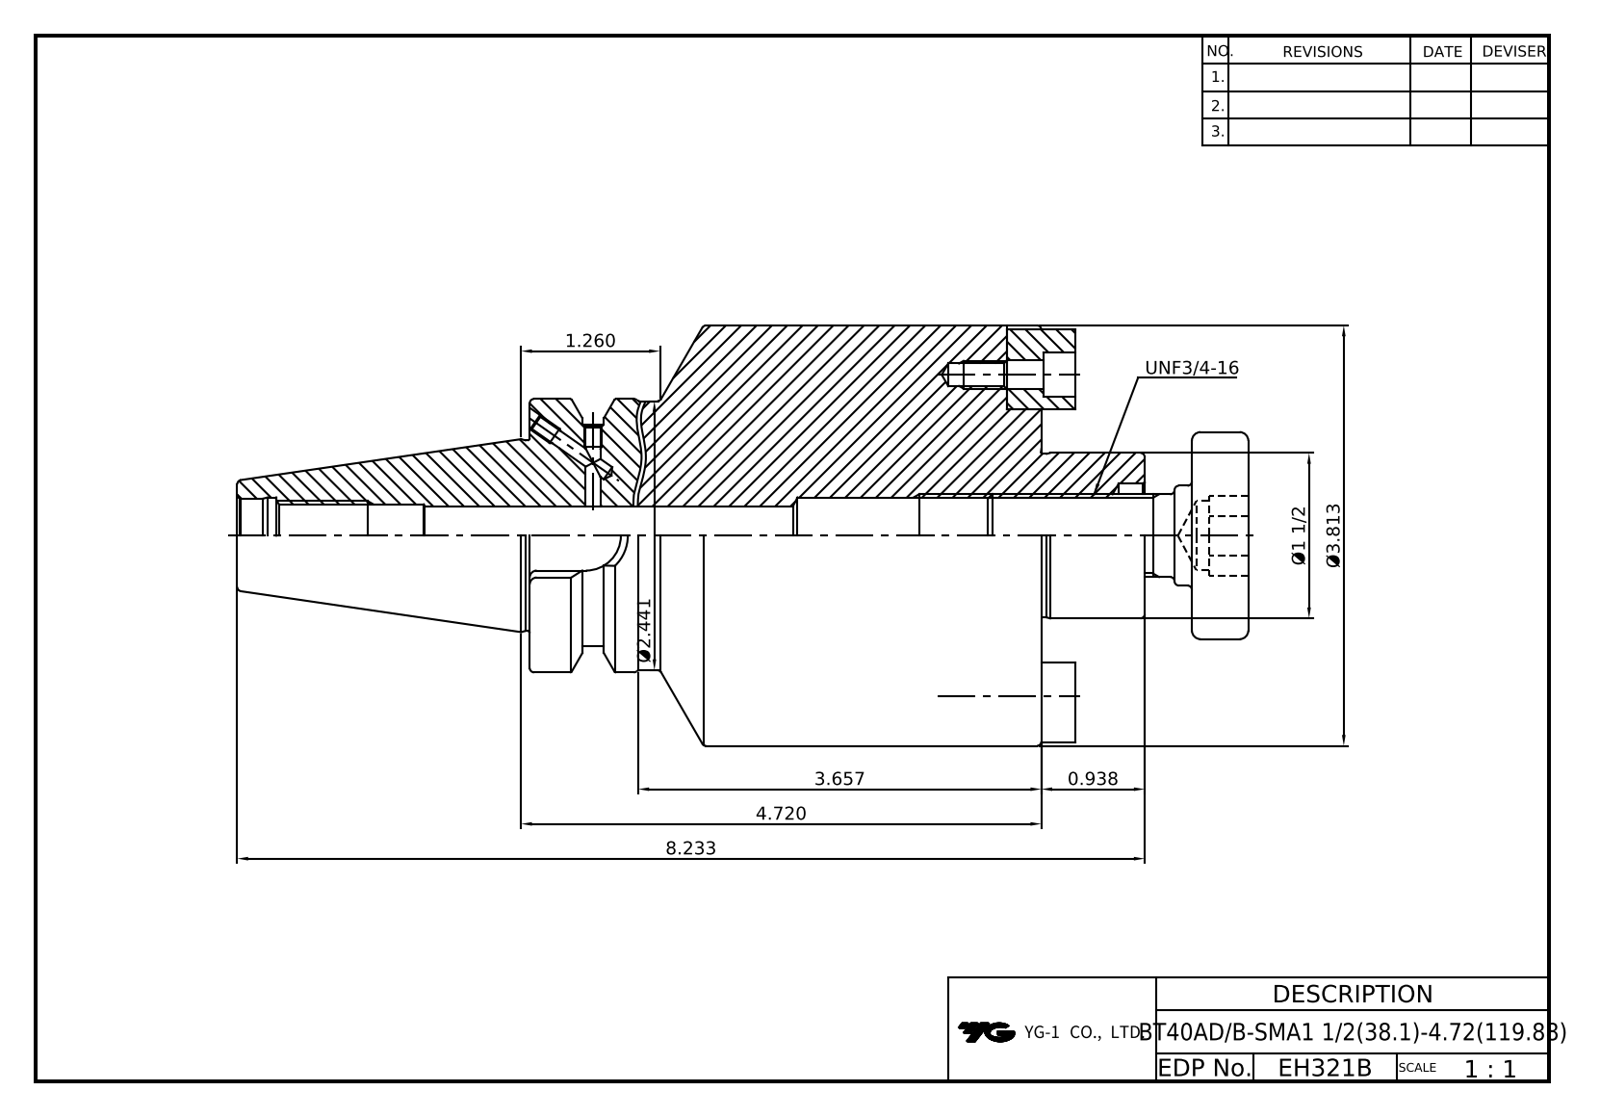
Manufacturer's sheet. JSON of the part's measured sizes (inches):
{"part_name": "LO-BT40ADB-SMA38.1-119.888; DRIVE KEY-15.875x15.875x18.5; HEX'' WRENCH BOLT-UNC1_4-20x5_8L; COLLAR BOLT-UNF3_4-16x47L", "step_written_by": "Autodesk Inventor 2025 (AP242_MANAGED_MODEL_BASED_3D_ENGINEERING_MIM_LF)", "units": "inches", "bodies": {"solids": 6, "faces": 151, "planar": 71, "cylindrical": 46, "other": 34}, "overall_size": [9.335, 3.813, 3.813], "volume_in3": 48.63, "surface_area_in2": 125.6, "round_holes": [[0.128, 4], [0.157, 4], [0.196, 2], [0.26, 2], [0.406, 2], [0.545, 1], [0.625, 1], [0.669, 1], [0.682, 1], [0.693, 1], [0.945, 1]], "round_bosses_or_shafts": [[0.375, 2], [0.25, 2], [3.813, 1], [2.48, 1], [2.441, 1], [2.071, 1], [1.878, 1], [1.732, 1]], "partial_cylinders_radius": [[0.312, 2], [0.317, 1]], "face_to_face_distances": [2.041, 1.529, 0.512, 4.641, 6.17, 6.682, 4.324, 0.318, 1.846, 2.358], "hole_center_spacings": [1.459, 2.918]}
